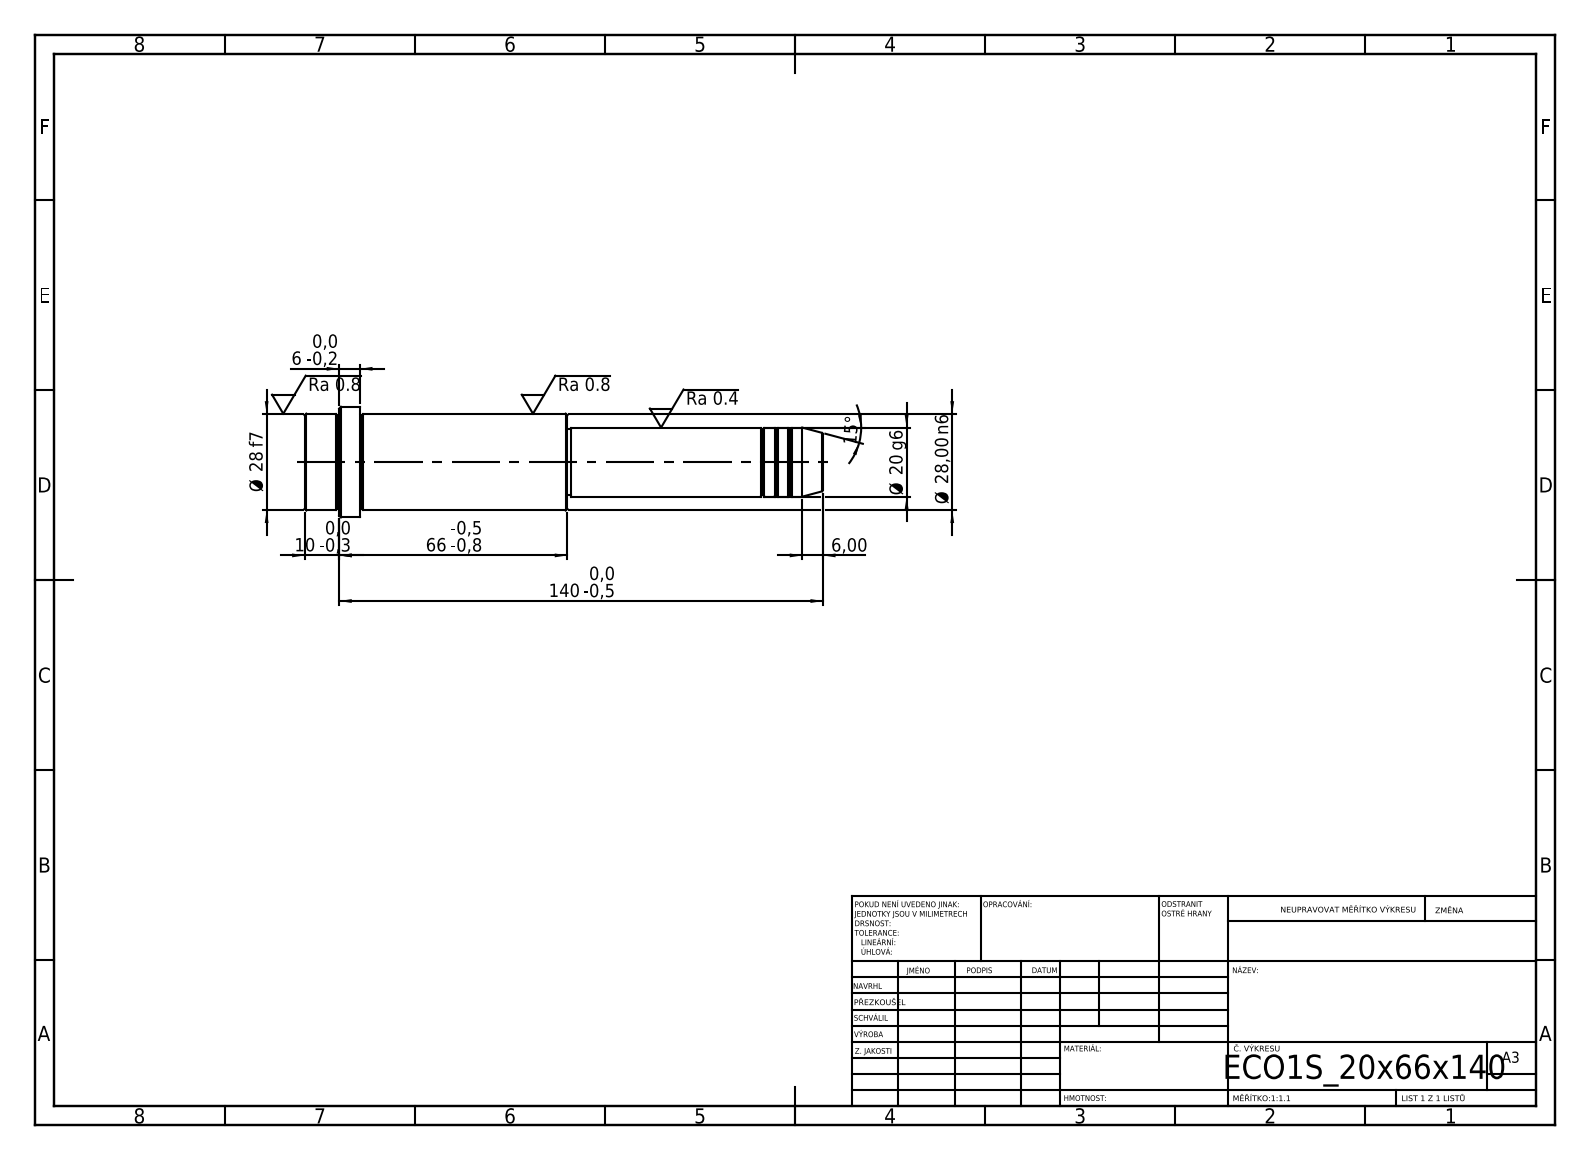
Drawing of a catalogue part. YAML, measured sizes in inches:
step_written_by: "SolidWorks 2019 (CONFIG_CONTROL_DESIGN)"
units: inches
bodies: {solids: 1, faces: 52, planar: 6, cylindrical: 16, other: 30}
overall_size: [5.906, 1.26, 1.26]
volume: 4.313
surface_area: 20.26
round_bosses_or_shafts:
  - {diameter: 1.26, count: 1}
  - {diameter: 1.102, count: 1}
  - {diameter: 0.787, count: 1}
  - {diameter: 0.748, count: 1}
face_to_face_distances: [2.992, 2.913, 5.906, 5.276, 2.362, 0.63, 5.512, 2.598, 0.236, 0.394]
